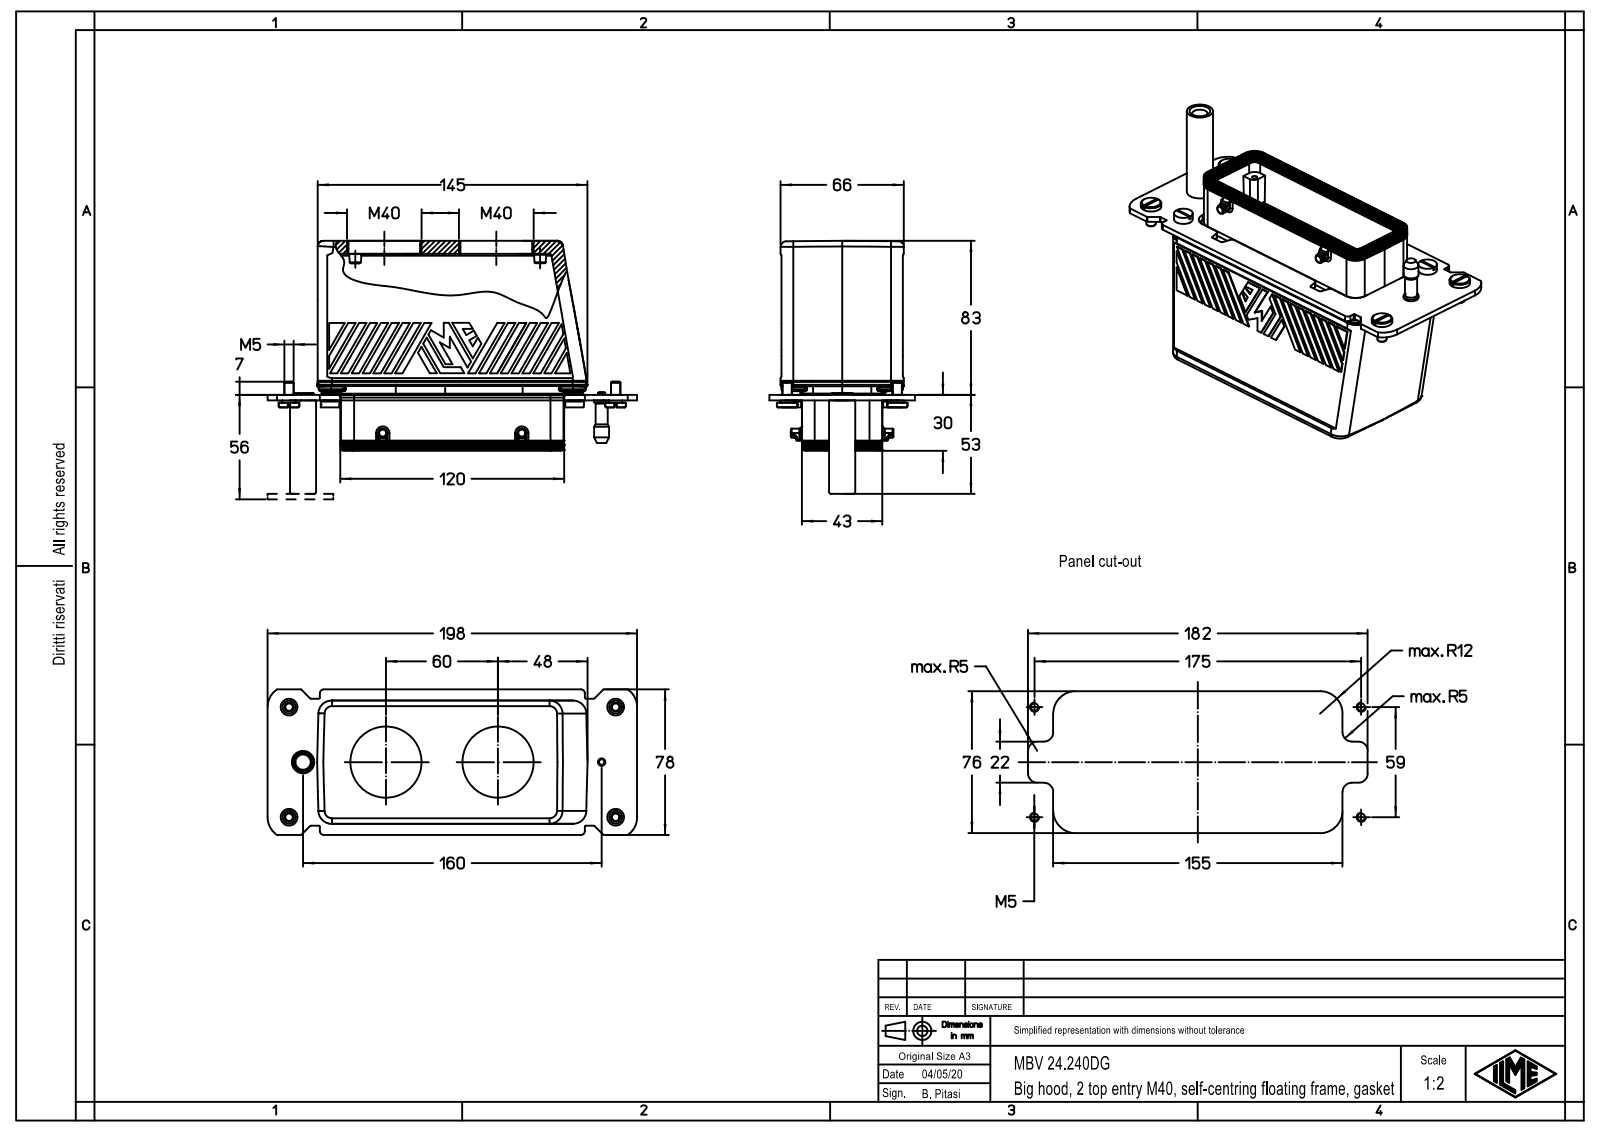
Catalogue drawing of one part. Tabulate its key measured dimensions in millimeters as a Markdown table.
| quantity | value |
| --- | --- |
| part name | MBV 24.240DG |
| STEP written by | Creo Elements/Direct Modeling 20.1B 02-Apr-2019 (C) Parametric Technology GmbH (AUTOMOTIVE_DESIGN) |
| units | millimeters |
| bodies | 1 solid, 989 faces (509 planar, 252 cylindrical, 228 other) |
| overall size | 198 × 135.21 × 78 |
| volume | 721 189 mm³ |
| surface area | 106 066 mm² |
| round holes (diameter × count) | 9 × 4, 5.1 × 2, 7.2 × 2, 40 × 2, 4.05 × 1, 8.2 × 1, 9.6 × 1, 12.05 × 1 |
| round bosses / shafts (diameter × count) | 5 × 6, 11 × 4, 7 × 4, 10 × 2, 9.3 × 2, 4.8 × 2, 14 × 1, 12 × 1 |
| partial cylindrical surfaces (radius × count) | 1 × 52, 0.5 × 20, 7 × 20, 2 × 14, 3 × 10, 4.2 × 8, 0.3 × 6, 1.5 × 6 |
| main face-to-face distances | 3, 65.01, 54, 85.21, 82.21, 11.01, 0.4, 11.41, 54.4, 65.41 |
| hole center spacings | 30.44, 170.08, 22.14, 30.65, 58.98, 59, 60.63, 70.41 |
